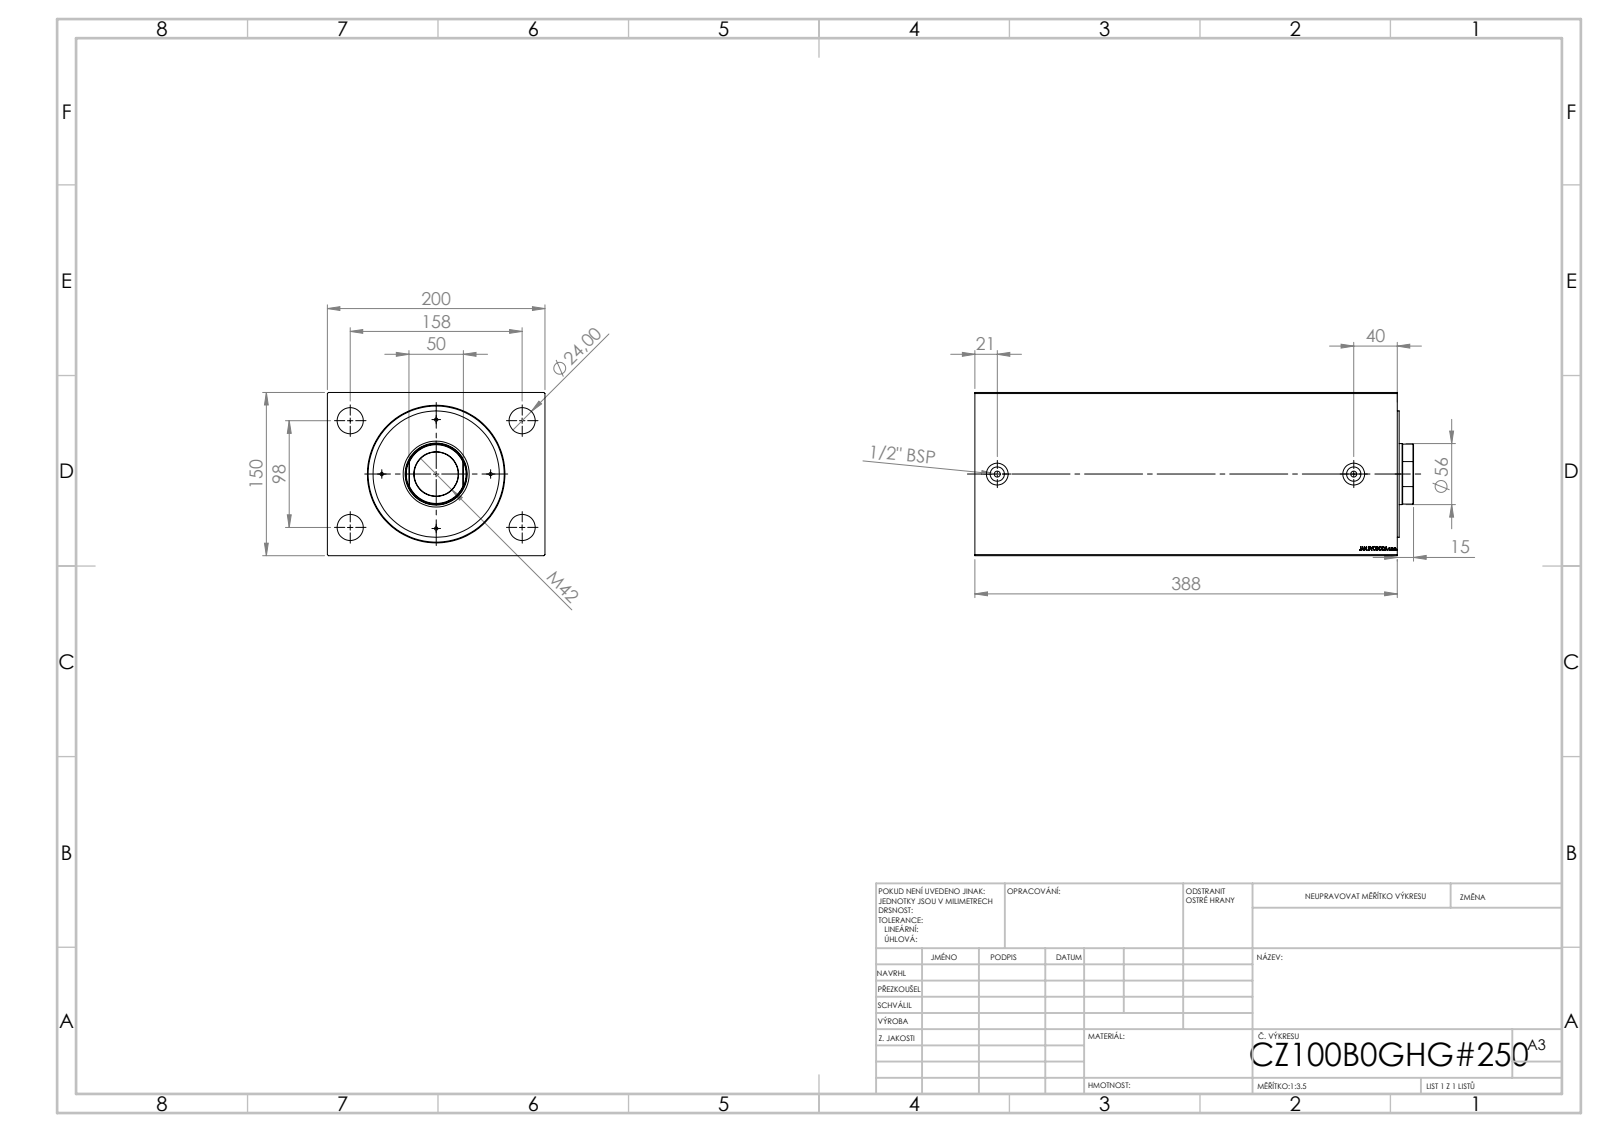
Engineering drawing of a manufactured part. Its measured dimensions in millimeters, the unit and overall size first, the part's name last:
Units: millimetres
Overall size (bounding box): 403 × 200 × 150
Round holes (diameter × count): ⌀3 ×4, ⌀24 ×4, ⌀5.5 ×2, ⌀13.16 ×2, ⌀20 ×2, ⌀36 ×1, ⌀40.5 ×1, ⌀56 ×1, ⌀57 ×1, ⌀100 ×1, ⌀125 ×1
Round bosses / shafts (diameter × count): ⌀116 ×1
Partial cylindrical surfaces — rounded edges, fillets, slot ends (radius × count): R27.5 ×1
Main face-to-face distances: 150, 200, 388, 354.7, 33.3, 15, 1.8, 13.2, 341.5, 374.8
Hole centre spacings: 50, 56.94, 70.71, 79.01, 92.96, 126.66, 137.99, 98
Volume: 10 130 000 mm³ · Surface area: 589 143 mm²
Bodies: 3 solids, 874 faces (400 planar, 58 cylindrical, 416 other)
Part name (STEP PRODUCT): V500CZ; V500CZ_B_VC
STEP written by: SolidWorks 2019 (CONFIG_CONTROL_DESIGN)
